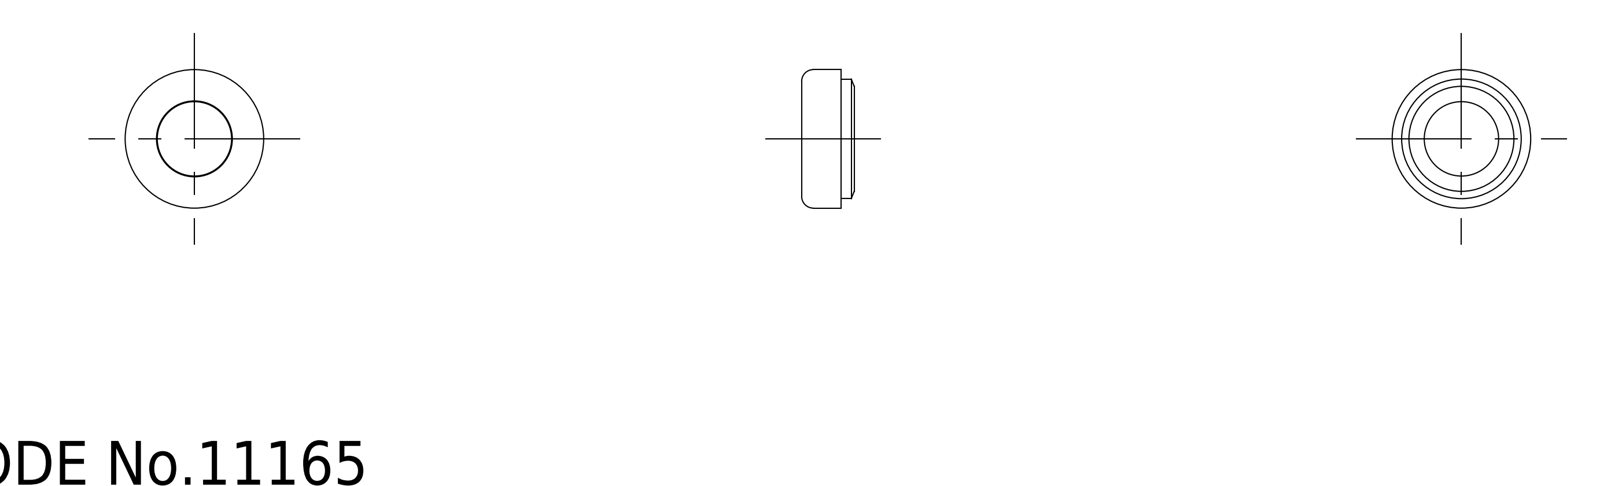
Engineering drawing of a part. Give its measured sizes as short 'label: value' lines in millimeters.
name: washer; packing; TL_421_M5
written by: SolidWorks 2015 (AUTOMOTIVE_DESIGN)
unit: mm
bodies: 2 solids, 22 faces (6 planar, 12 cylindrical, 4 other)
size: 9.5 × 9.5 × 3.6
volume: 160 mm³; area: 405 mm²
holes: 1× ⌀5.1, 1× ⌀5.2, 1× ⌀7.9
bosses: 1× ⌀9.5, 1× ⌀8.2
face distances: 0.8, 2.7, 1.9, 3.6, 2.8, 0.9
